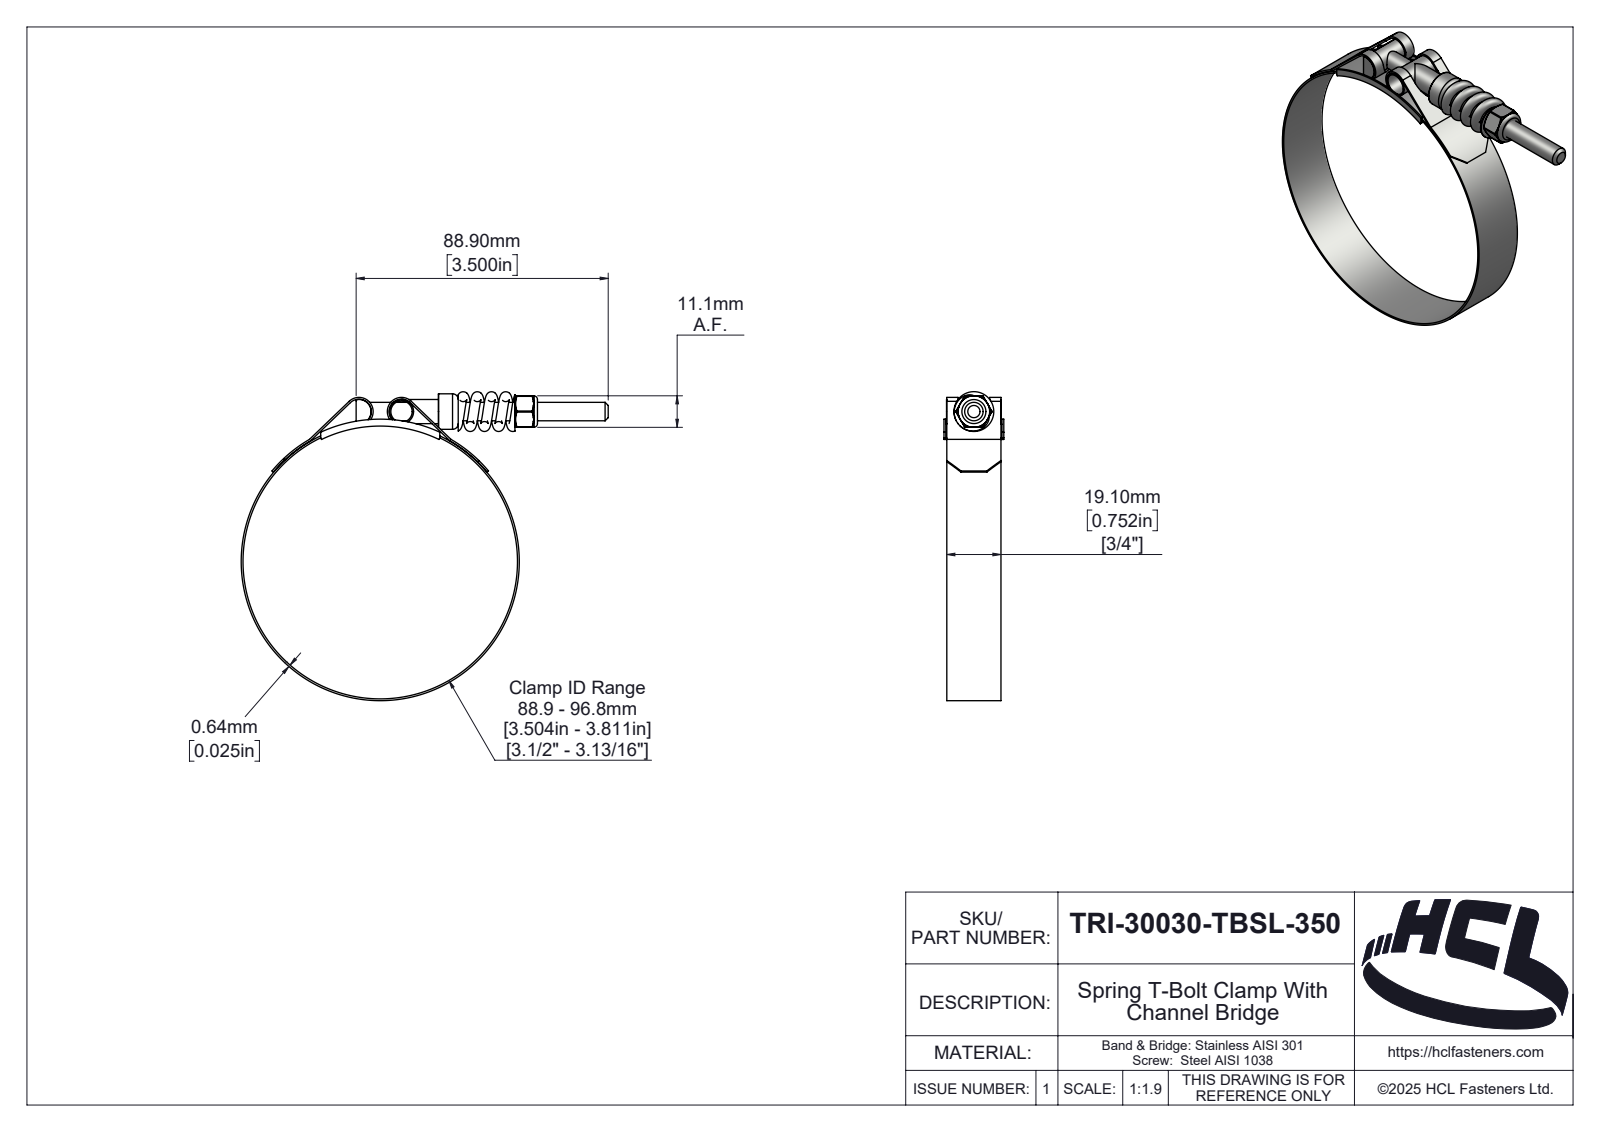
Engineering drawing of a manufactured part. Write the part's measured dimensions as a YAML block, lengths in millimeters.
part_name: "TRI-30030-TBSL-350"
step_written_by: "SolidWorks 2025 (AUTOMOTIVE_DESIGN)"
units: millimeters
bodies: {solids: 7, faces: 332, planar: 48, cylindrical: 122, other: 162}
overall_size: [130.44, 108.93, 21.1]
volume: 11653
surface_area: 23577
round_holes:
  - {diameter: 5.4, count: 1}
  - {diameter: 6.35, count: 1}
  - {diameter: 6.5, count: 1}
  - {diameter: 7.52, count: 1}
  - {diameter: 96.8, count: 1}
round_bosses_or_shafts:
  - {diameter: 8.52, count: 2}
  - {diameter: 98.08, count: 1}
  - {diameter: 12.52, count: 1}
partial_cylinders:
  - {radius: 0.39, count: 6}
  - {radius: 0.5, count: 2}
  - {radius: 4.36, count: 2}
  - {radius: 5, count: 2}
  - {radius: 0.59, count: 1}
  - {radius: 2.42, count: 1}
  - {radius: 3.03, count: 1}
  - {radius: 3.19, count: 1}
face_to_face_distances: [0.64, 19.1, 1, 20.1, 20.46, 0.36, 19.46, 56, 21.1, 20.2]
hole_center_spacings: [53.4]
